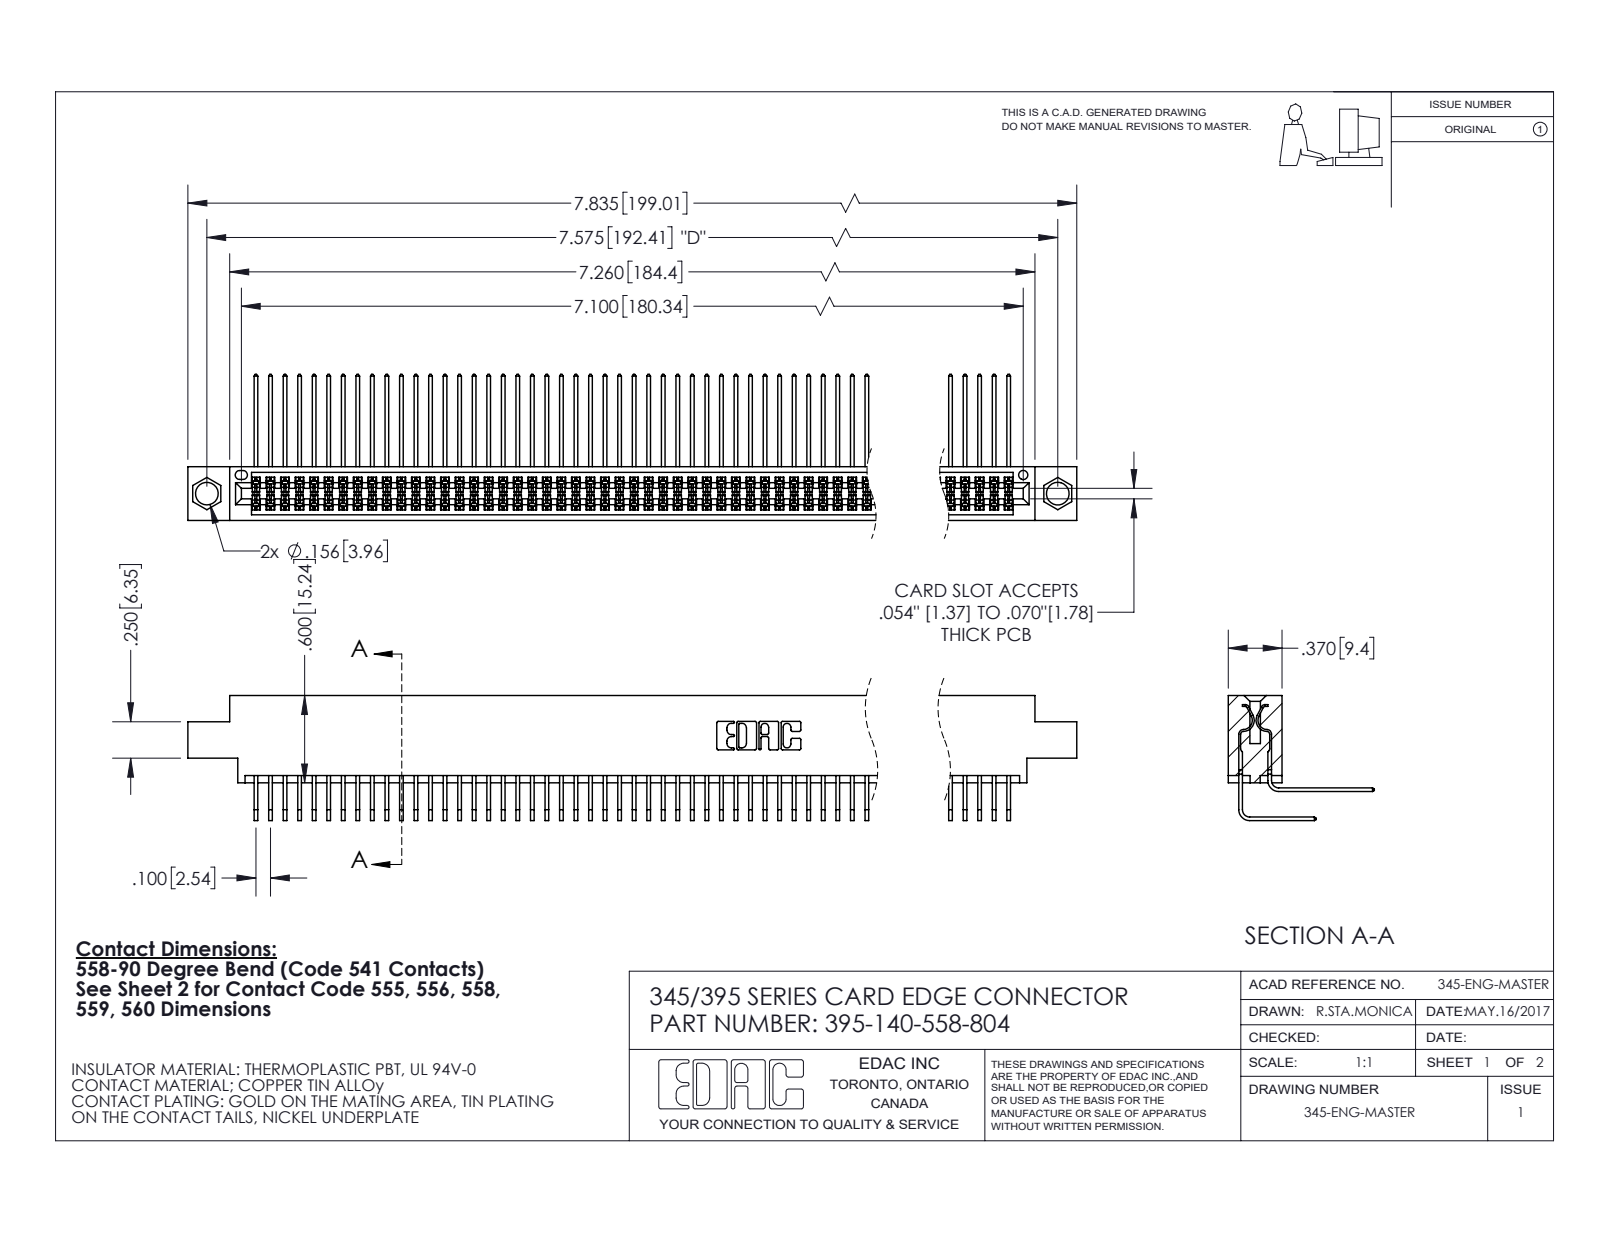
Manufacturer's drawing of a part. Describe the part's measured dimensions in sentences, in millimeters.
The part is named "345-292-001_558 559 Tail - 1; 395-140-558-804; 345-292-001_558 Tail - 2; 345 Part_0.170 Offset - 0.156 Dia-TI". Its 3-D file was written by "SolidWorks 2020 (CONFIG_CONTROL_DESIGN)". It is 141 solids with 7424 faces: 4998 planar, 2426 cylindrical and 0 other. Overall it measures 199 by 25.5 by 21.8 millimeters. Its volume is 20 170 cubic millimeters and its surface area 34 170 square millimeters. Round holes: 2 of diameter 4, 1 of diameter 1.6. Partial cylindrical surfaces (rounded edges, fillets, slot ends): 210 of radius 0.2, 22 of radius 0.3, 6 of radius 0.2, 6 of radius 0.8, 3 of radius 0.7, 2 of radius 0.4, 2 of radius 0.5, 2 of radius 0.6. The main face-to-face distances are 1.8, 7.6, 5.1, 9.4, 2.5, 6.9, 0.6, 5.7, 4.4, 0.6. The hole center spacings are 6.9, 186.4, 192.4.
